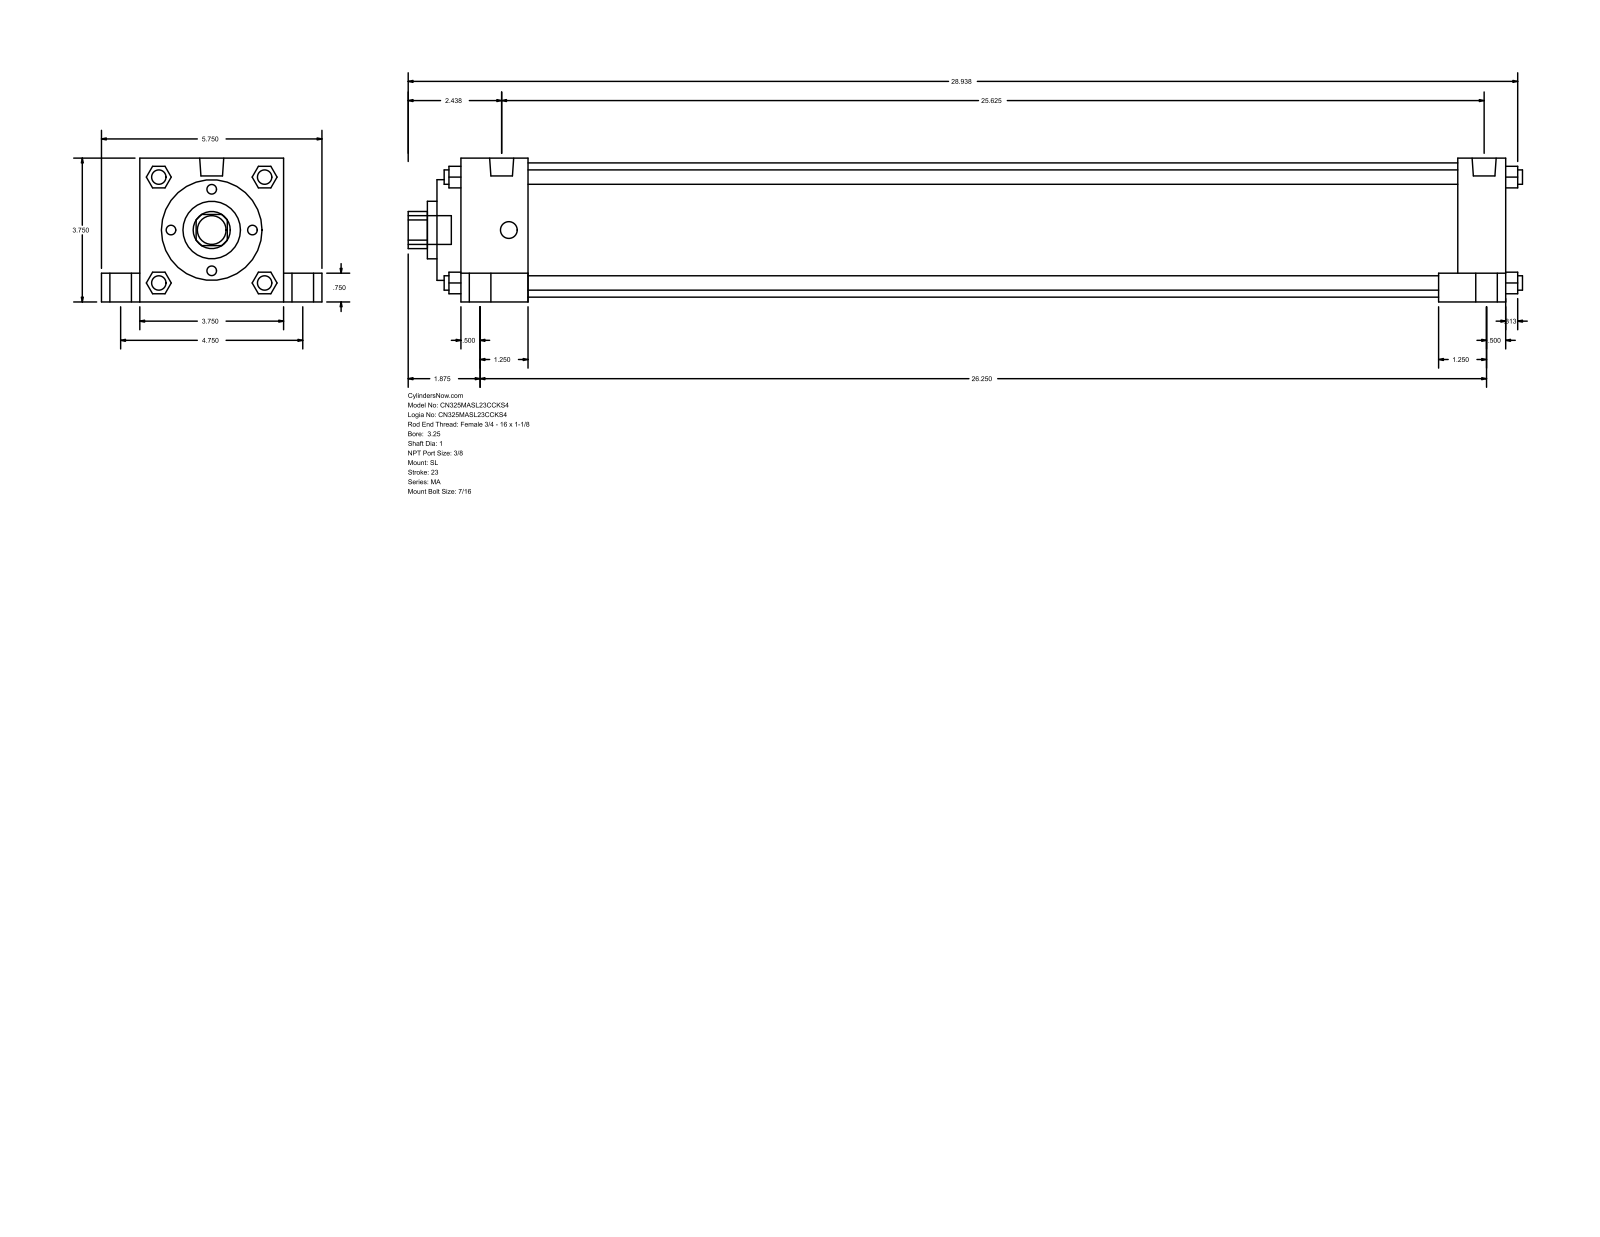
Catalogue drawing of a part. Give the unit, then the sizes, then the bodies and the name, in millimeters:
Units: millimetres
Overall size (bounding box): 738.19 × 146.05 × 95.25
Round holes (diameter × count): ⌀25.4 ×1, ⌀38.1 ×1, ⌀66.67 ×1, ⌀88.9 ×1
Round bosses / shafts (diameter × count): ⌀20.64 ×4, ⌀14.29 ×4, ⌀11.11 ×4, ⌀9.53 ×4, ⌀15.93 ×2, ⌀19.05 ×1
Partial cylindrical surfaces — rounded edges, fillets, slot ends (radius × count): R12.29 ×1
Main face-to-face distances: 95.24, 692.16, 615.95, 15.87, 25.41, 120.65, 19.05, 660.41, 31.75, 44.46
Bodies: 0 solids, 150 faces (113 planar, 37 cylindrical, 0 other)
Part name (STEP PRODUCT): MA_SL__0325_1
STEP written by: GSSL Pune (CONFIG_CONTROL_DESIGN)
